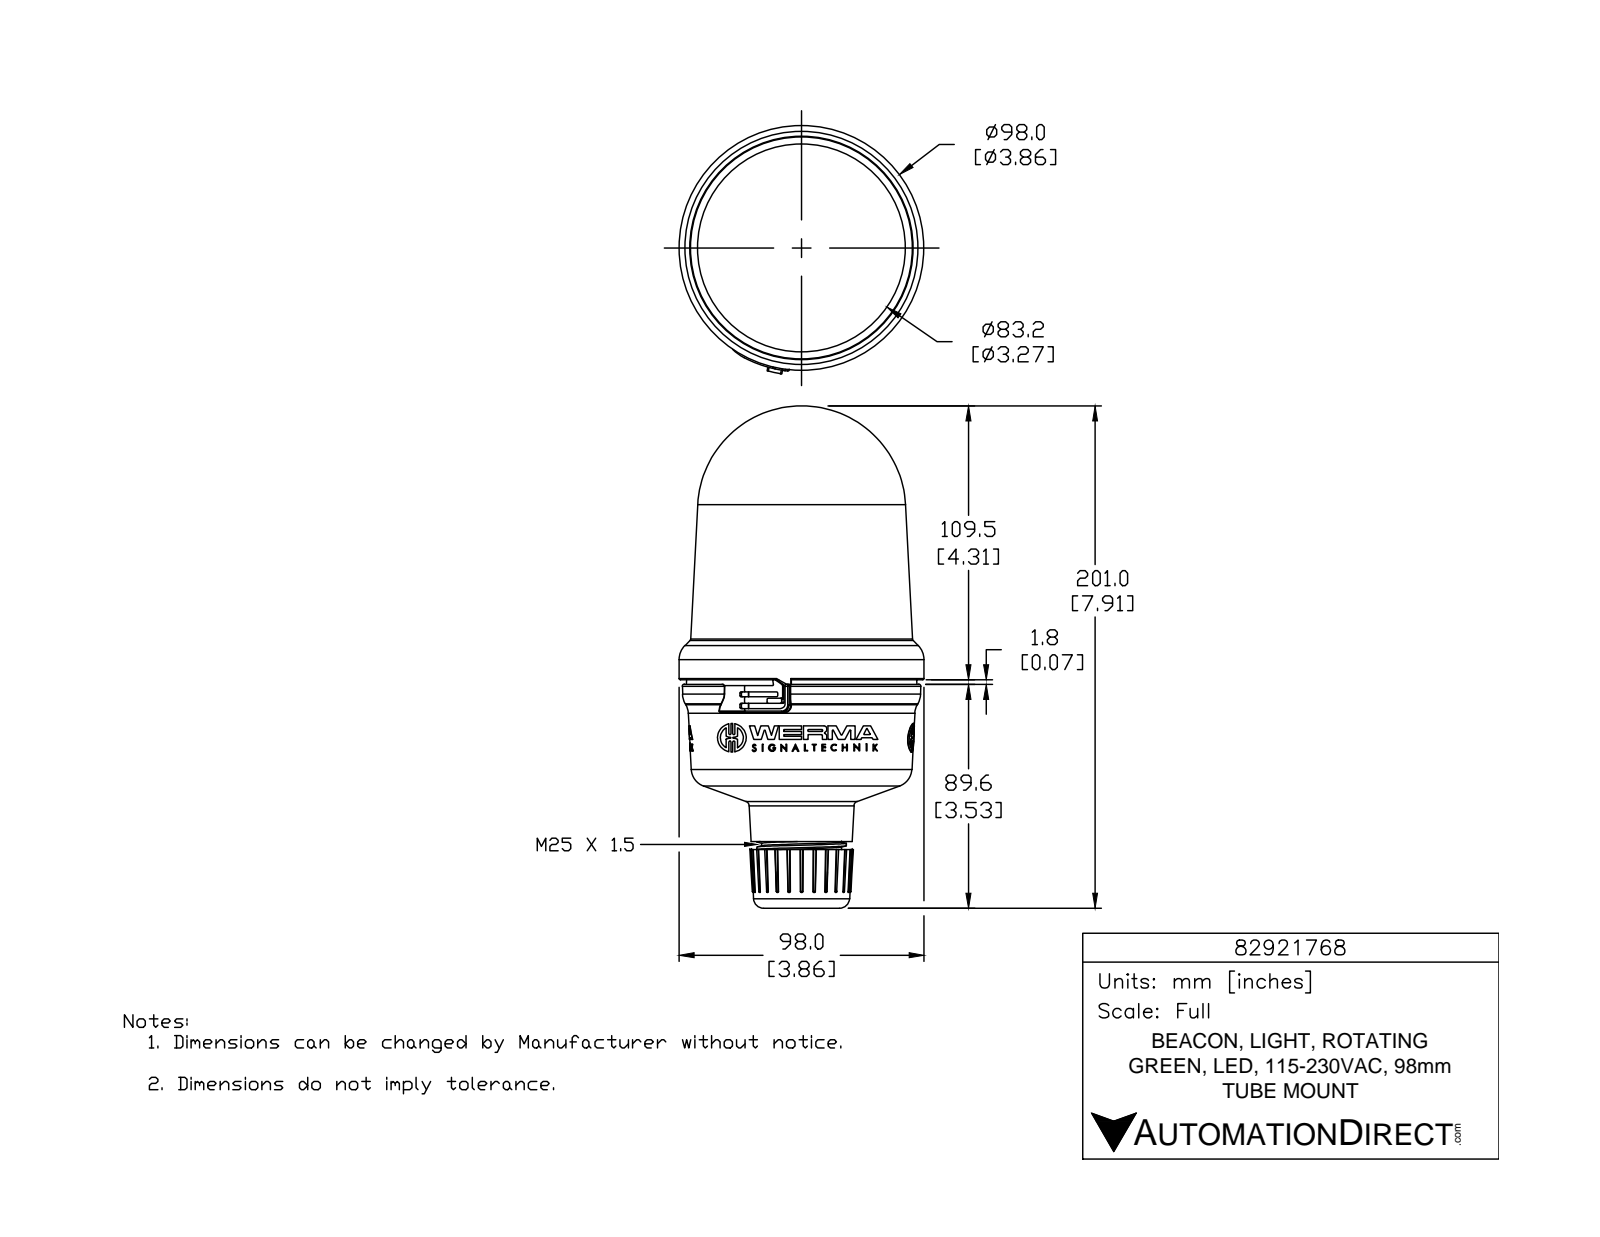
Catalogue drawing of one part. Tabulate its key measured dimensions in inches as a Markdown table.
| quantity | value |
| --- | --- |
| part name | 82921768 |
| STEP written by | SolidWorks 2015 (AUTOMOTIVE_DESIGN) |
| units | inches |
| bodies | 1 solid, 1006 faces (554 planar, 189 cylindrical, 263 other) |
| overall size | 7.914 × 3.912 × 3.858 |
| volume | 54.7 in³ |
| surface area | 91.39 in² |
| round holes (diameter × count) | 0.078 × 3, 1.013 × 1, 1.024 × 1 |
| round bosses / shafts (diameter × count) | 0.452 × 3, 0.113 × 3, 3.858 × 1, 1.409 × 1, 1.261 × 1 |
| partial cylindrical surfaces (radius × count) | 0.02 × 12, 0.007 × 9, 0.007 × 6, 0.016 × 6, 0.016 × 6, 0.016 × 6, 0.262 × 6, 0.006 × 3 |
| main face-to-face distances | 2.214, 0.462, 2.676, 0.335, 0.127, 2.548, 2.603, 2.476, 2.141, 0.073 |
